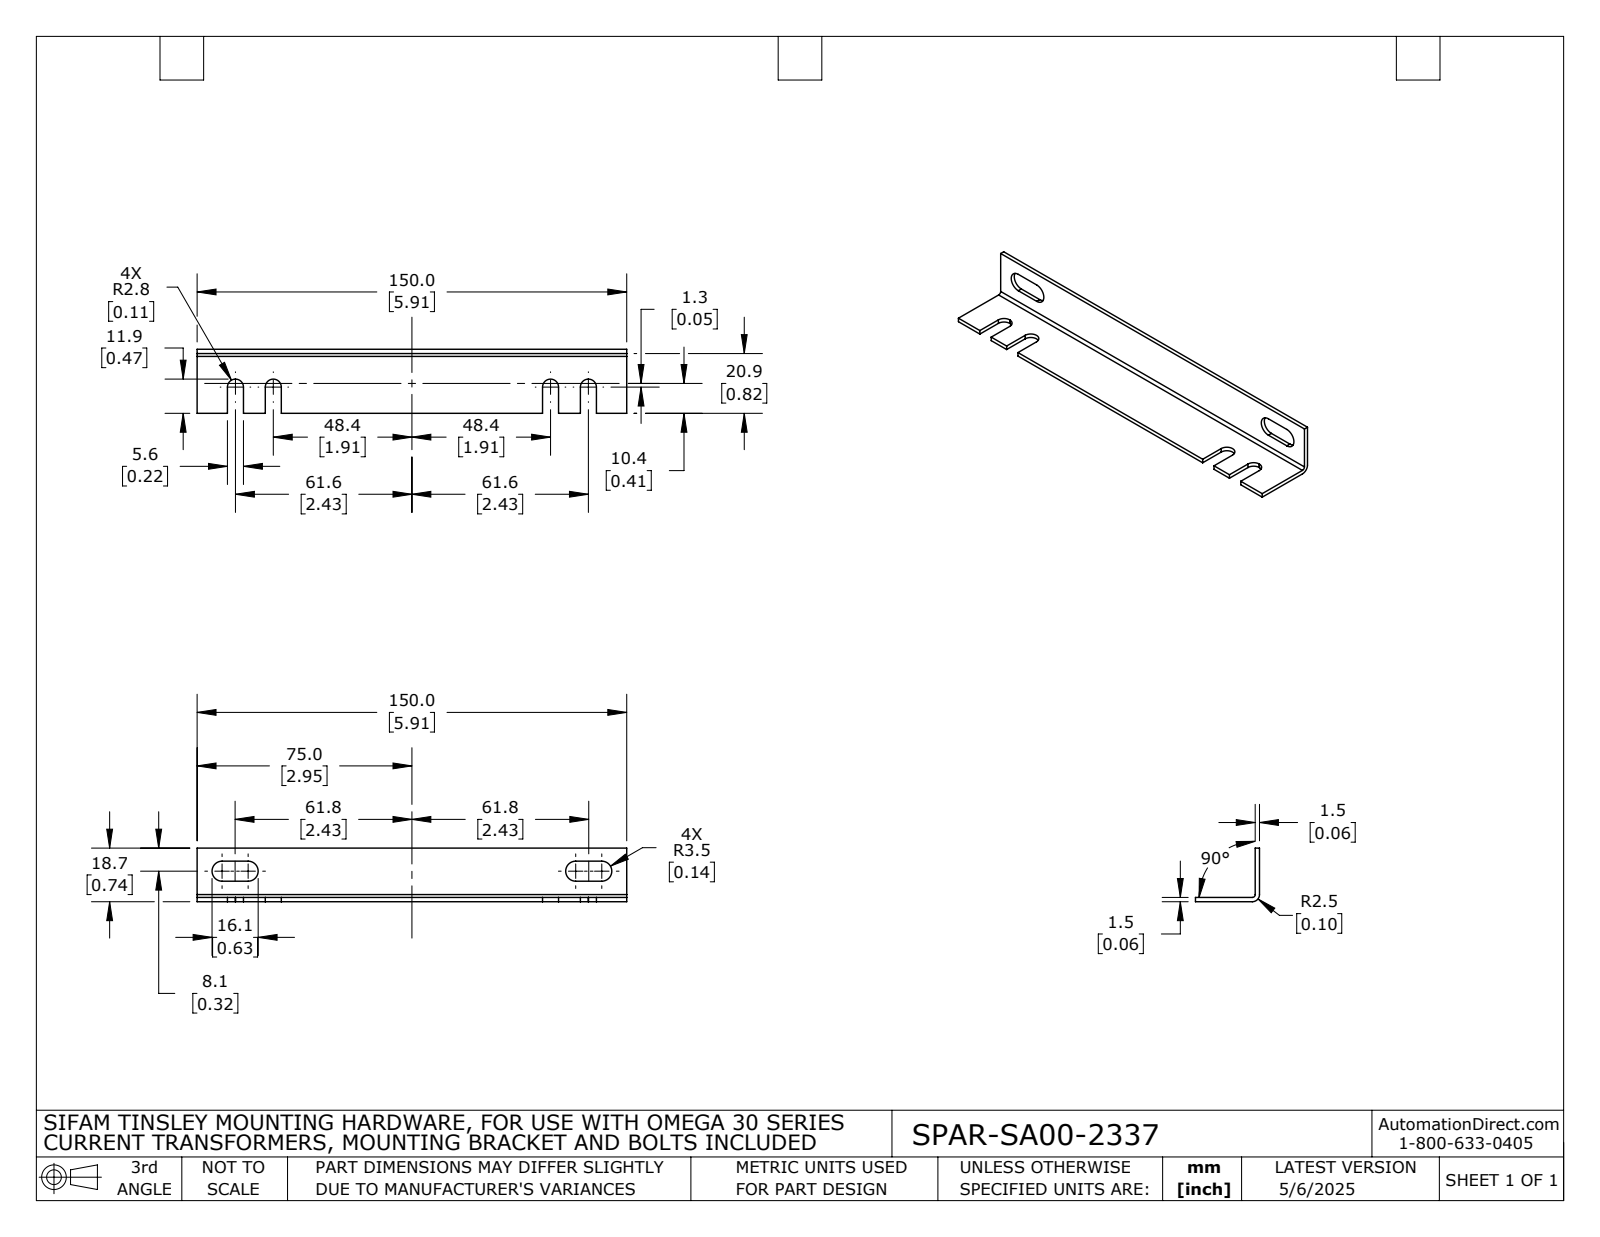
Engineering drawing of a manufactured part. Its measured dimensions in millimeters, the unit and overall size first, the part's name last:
Units: millimetres
Overall size (bounding box): 150 × 72.4 × 18.7
Partial cylindrical surfaces — rounded edges, fillets, slot ends (radius × count): R2.8 ×12, R3.5 ×4, R1 ×2, R2.5 ×2
Main face-to-face distances: 1.5, 50, 51.5, 48.5, 18.7, 17.2, 22.4, 20.9, 72.4, 70.9
Volume: 16 100 mm³ · Surface area: 23 100 mm²
Bodies: 2 solids, 80 faces (52 planar, 28 cylindrical, 0 other)
Part name (STEP PRODUCT): SPAR-SA00-2337
STEP written by: SolidWorks 2021 (AUTOMOTIVE_DESIGN)
